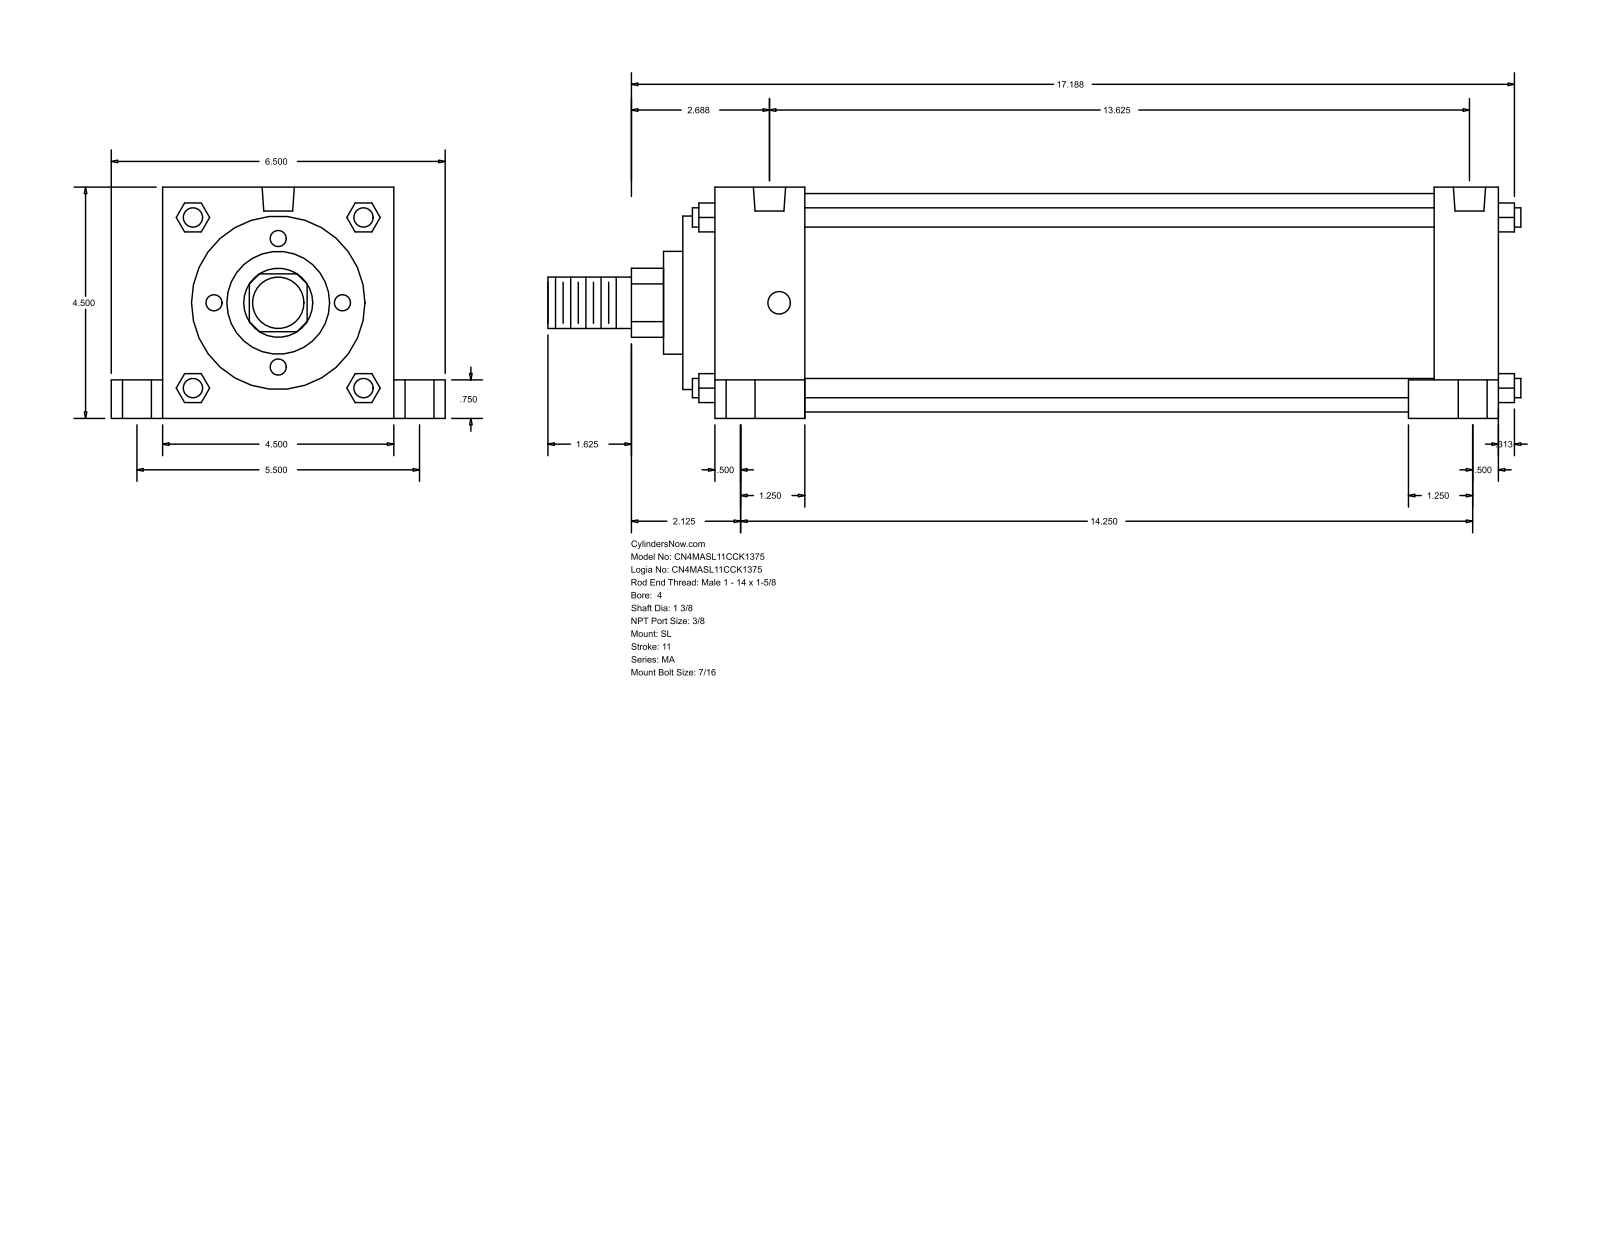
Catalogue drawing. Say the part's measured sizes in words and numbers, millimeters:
The part is named "MA_SL__0400_1.375". Its 3-D file was written by "GSSL Pune (CONFIG_CONTROL_DESIGN)". It is 0 solids with 150 faces: 113 planar, 37 cylindrical and 0 other. Overall it measures 481.01 by 165.1 by 114.3 millimeters. Round holes: 4 of diameter 11.11, 4 of diameter 14.29, 4 of diameter 20.64, 2 of diameter 15.93. Round bosses or shafts: 4 of diameter 9.53, 1 of diameter 107.95, 1 of diameter 85.72, 1 of diameter 50.8, 1 of diameter 34.92, 1 of diameter 25.4. Partial cylindrical surfaces (rounded edges, fillets, slot ends): 1 of radius 17.06. The main face-to-face distances are 114.3, 387.35, 403.22, 15.87, 60.32, 44.45, 342.9, 371.48, 355.61, 311.16. The hole center spacings are 4.77, 69.87, 70.14, 71.29, 72.4, 139.7, 336.54, 341.31.
